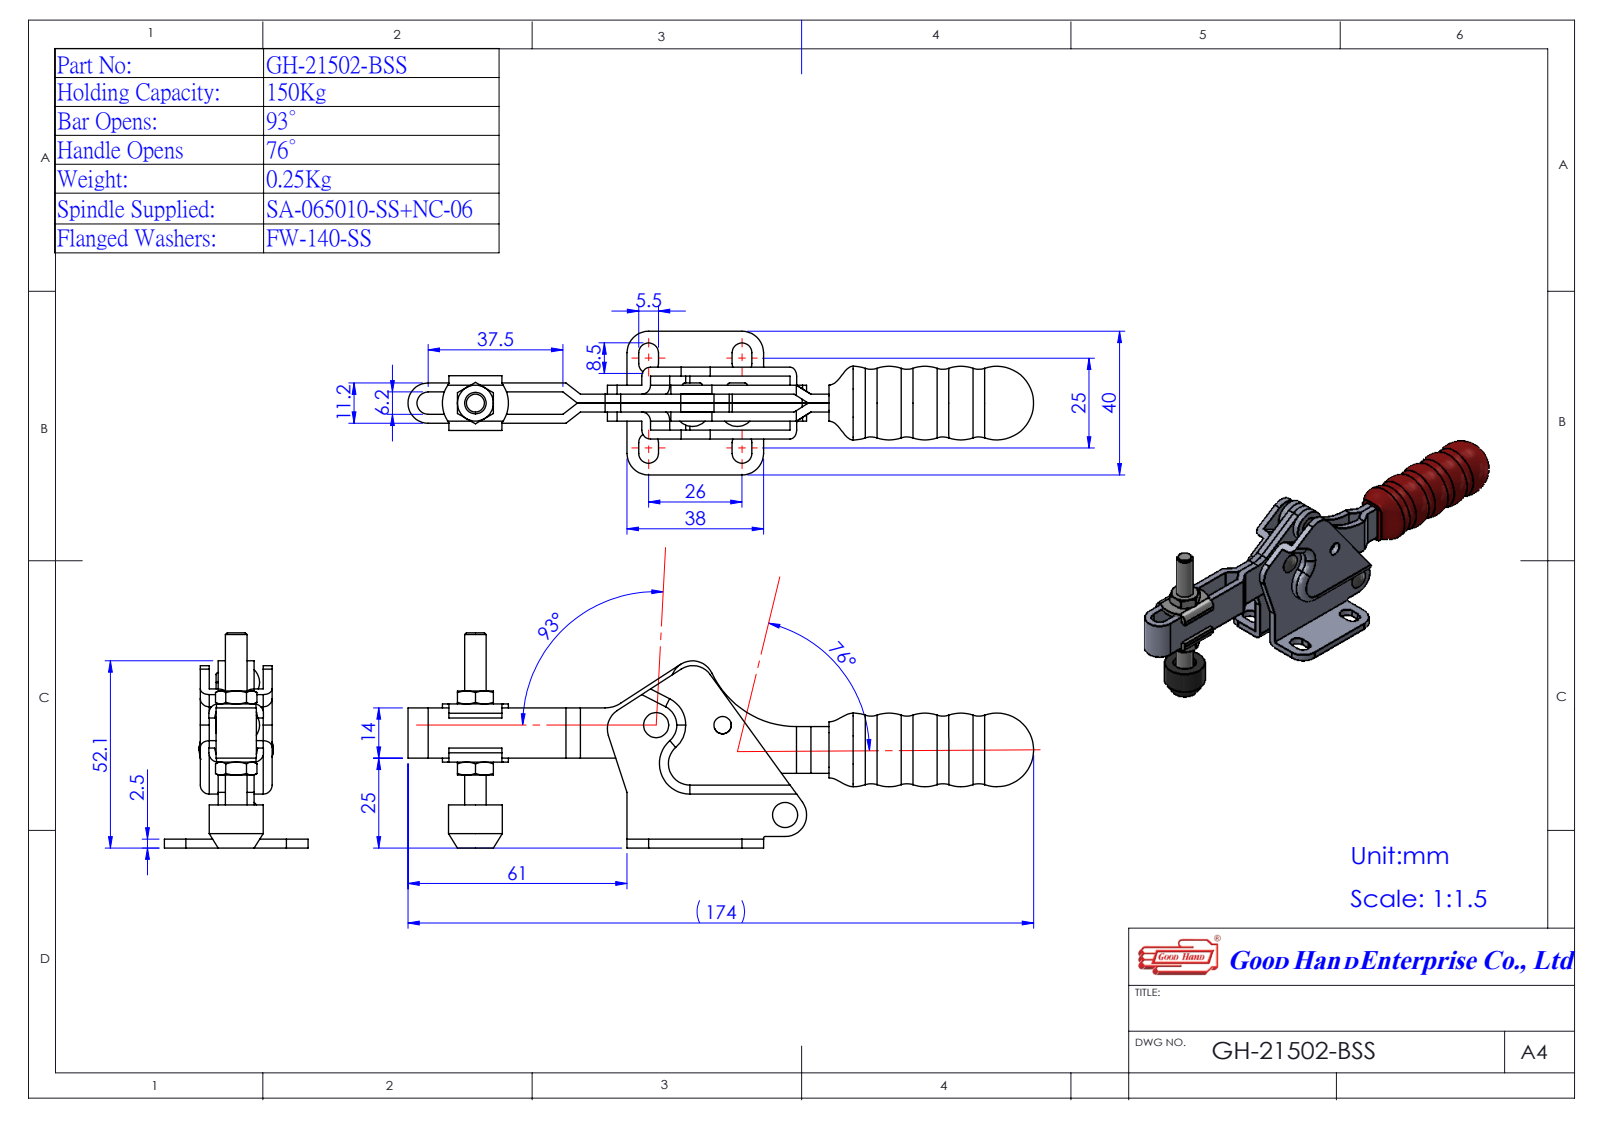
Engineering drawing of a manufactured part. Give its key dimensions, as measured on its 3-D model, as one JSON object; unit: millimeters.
{"part_name": "121502B08-1^493785(GH-21502-B); 493785(GH-21502-B); Group5^493785(GH-21502-B); Group4^493785(GH-21502-B) (+2 more)", "step_written_by": "SolidWorks 2016 (AUTOMOTIVE_DESIGN)", "units": "millimeters", "bodies": {"solids": 5, "faces": 304, "planar": 132, "cylindrical": 108, "other": 64}, "overall_size": [181, 59.9, 40], "volume_mm3": 54989, "surface_area_mm2": 31335, "round_holes": [[3, 4]], "round_bosses_or_shafts": [[4.85, 2], [15, 1], [6, 1]], "partial_cylinders_radius": [[6, 10], [2.75, 8], [1, 7], [2.6, 4], [8, 2], [0.5, 1], [3.1, 1], [5.6, 1]], "face_to_face_distances": [2.5, 5, 7.5, 10, 12.5, 15, 3.1, 4.4, 13.1, 1.9], "hole_center_spacings": [15.61, 22.06, 22.99, 23.78, 43.75, 45.02]}
